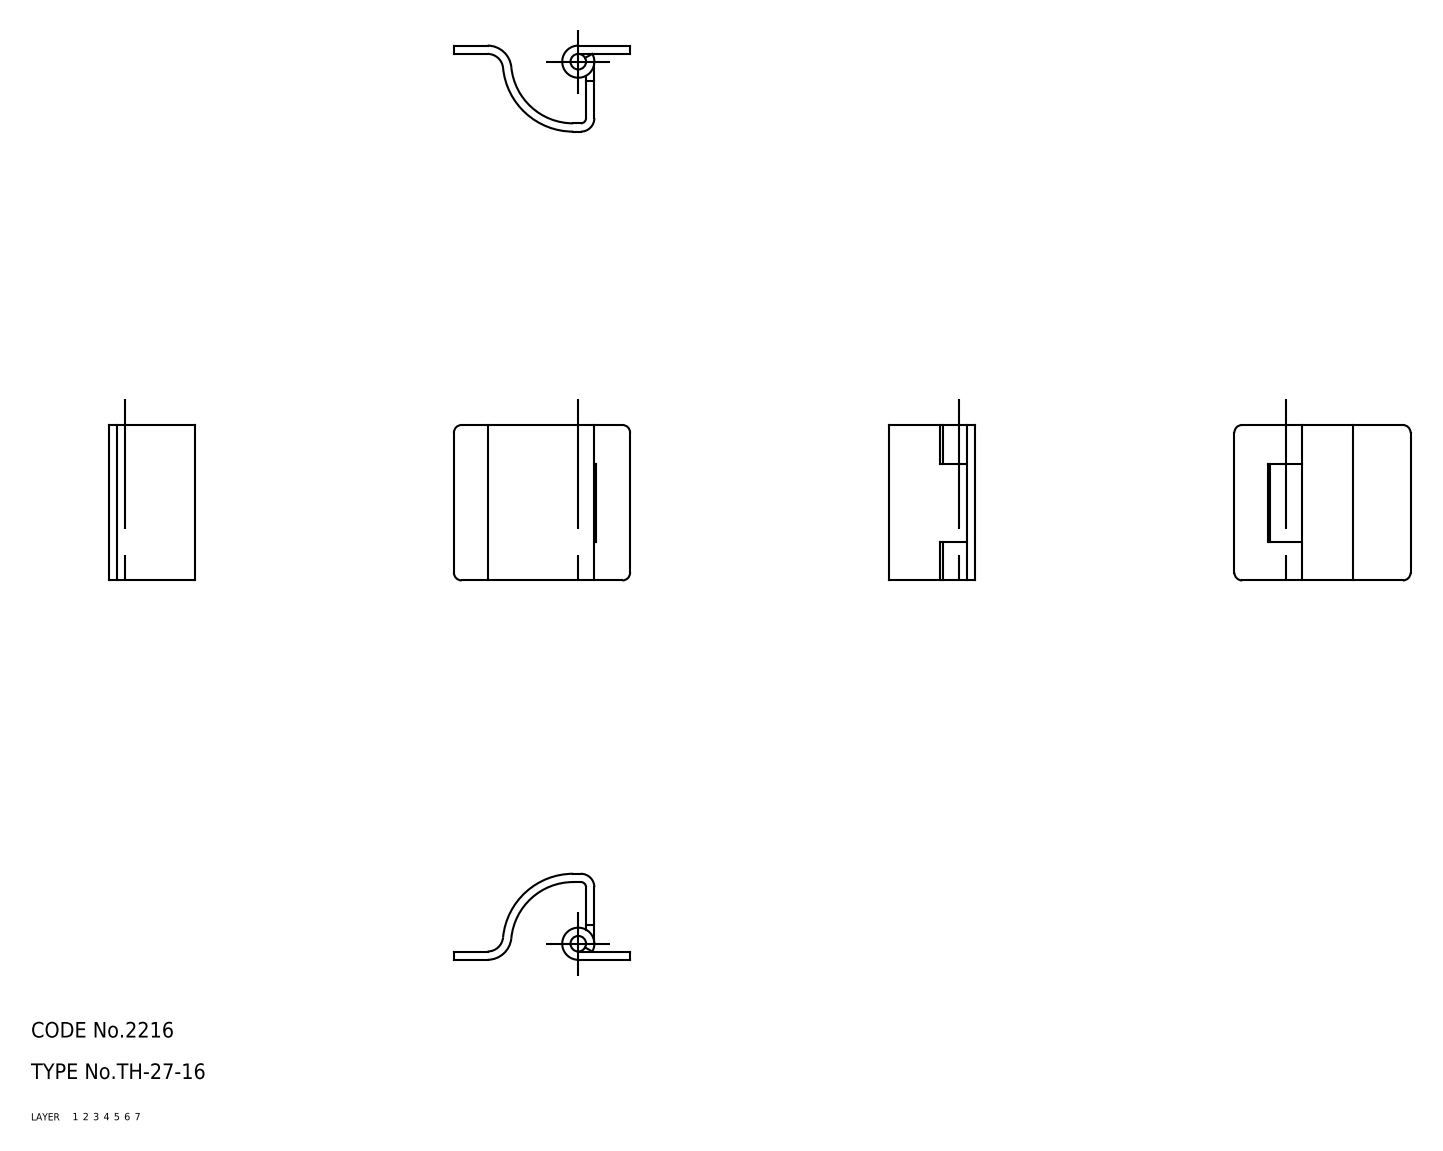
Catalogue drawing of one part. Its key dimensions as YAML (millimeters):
part_name: "shaft; hinge piece_B; hinge piece_A; TH_27_16_6874_36"
step_written_by: "CADfix (AUTOMOTIVE_DESIGN)"
units: millimeters
bodies: {solids: 3, faces: 44, planar: 0, cylindrical: 0, other: 44}
overall_size: [34, 30, 16.6]
volume: 3307
surface_area: 4659
